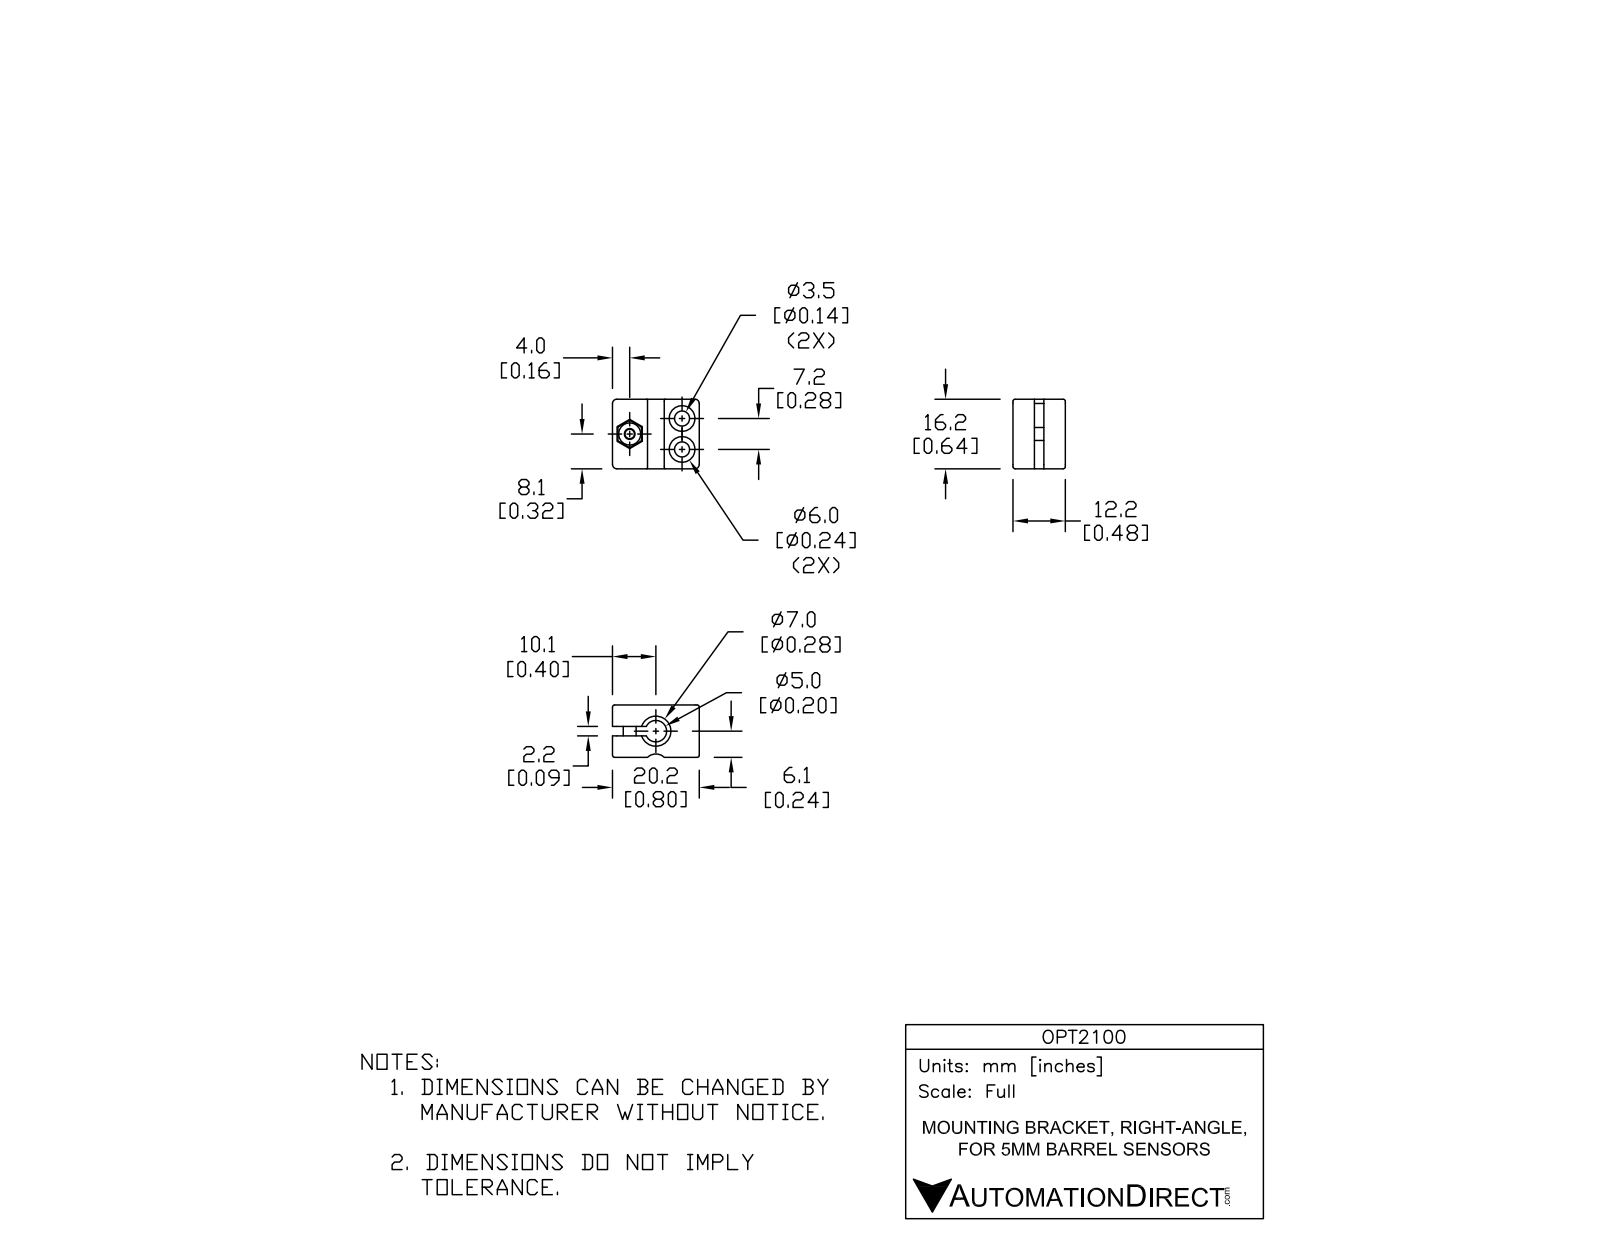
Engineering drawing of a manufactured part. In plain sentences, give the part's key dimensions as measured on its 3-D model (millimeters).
The part is named "1012460_GEHAEUSE_BSM5NB". Its 3-D file was written by "Unknown (CONFIG_CONTROL_DESIGN)". It is 1 solid with 85 faces: 44 planar, 27 cylindrical and 14 other. Overall it measures 20.2 by 16.2 by 12.2 millimeters. Its volume is 2 842 cubic millimeters and its surface area 2 421 square millimeters. Round holes: 2 of diameter 3.5, 2 of diameter 6, 1 of diameter 2.5, 1 of diameter 5. Round bosses or shafts: 1 of diameter 5.5, 1 of diameter 3. Partial cylindrical surfaces (rounded edges, fillets, slot ends): 8 of radius 0.5, 4 of radius 1, 1 of radius 2.75. The main face-to-face distances are 7.2, 5, 16.2, 12.2, 20.2, 2.2, 5.88, 2, 3, 9.2. The hole center spacings are 12.72, 7.2.
